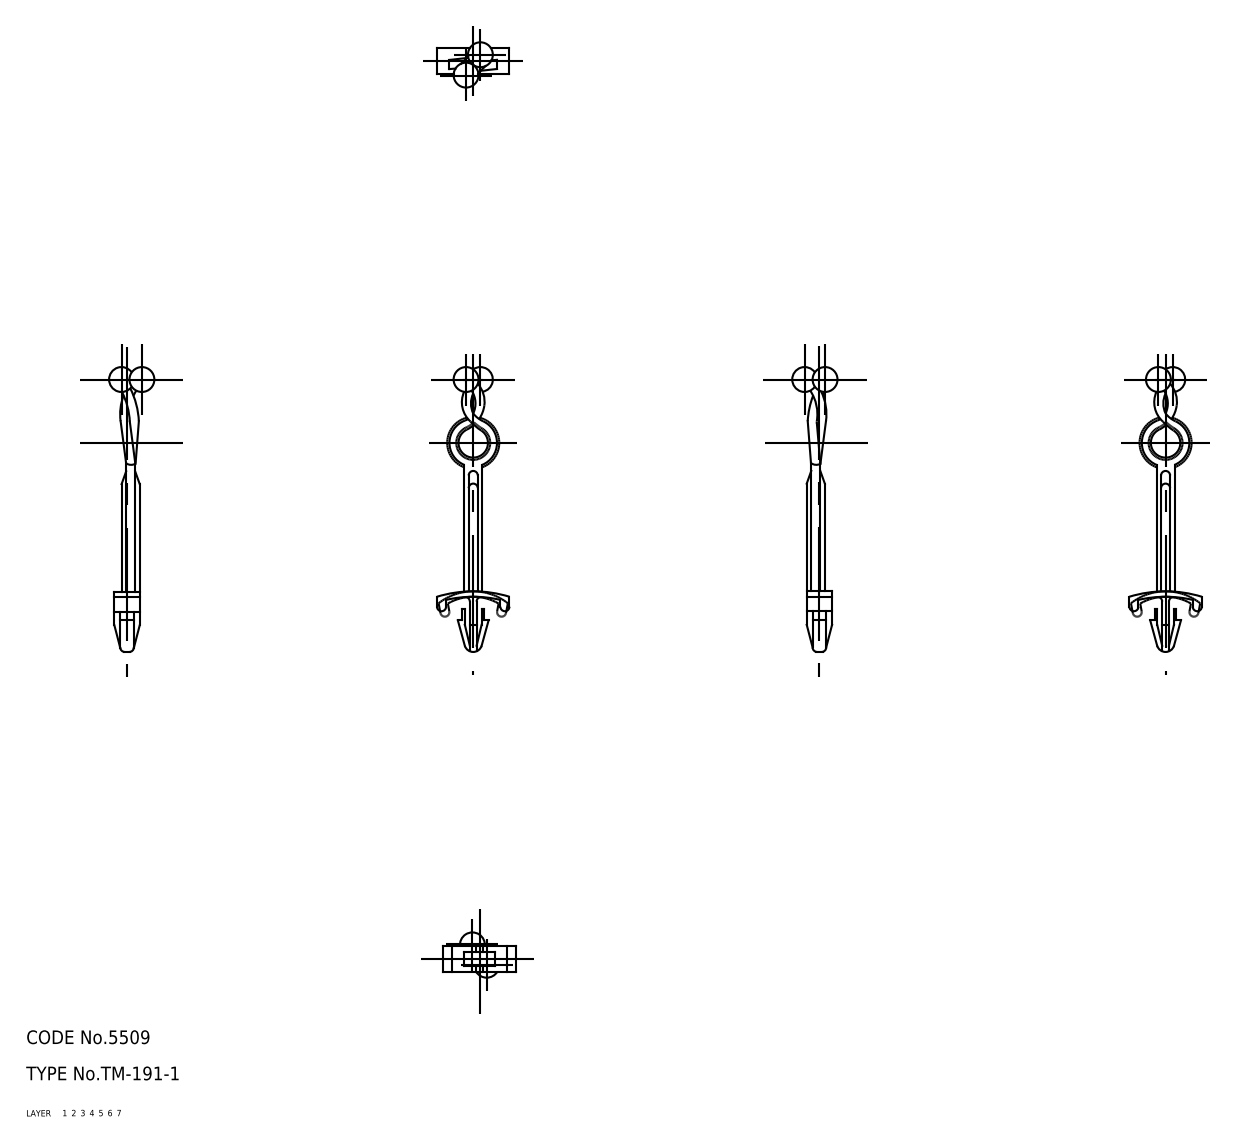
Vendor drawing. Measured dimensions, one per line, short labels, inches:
name: clip
written by: CADfix (AUTOMOTIVE_DESIGN)
unit: in
bodies: 1 solid, 73 faces (0 planar, 0 cylindrical, 73 other)
size: 2.478 × 0.63 × 0.412
volume: 0.06 in³; area: 2.404 in²
